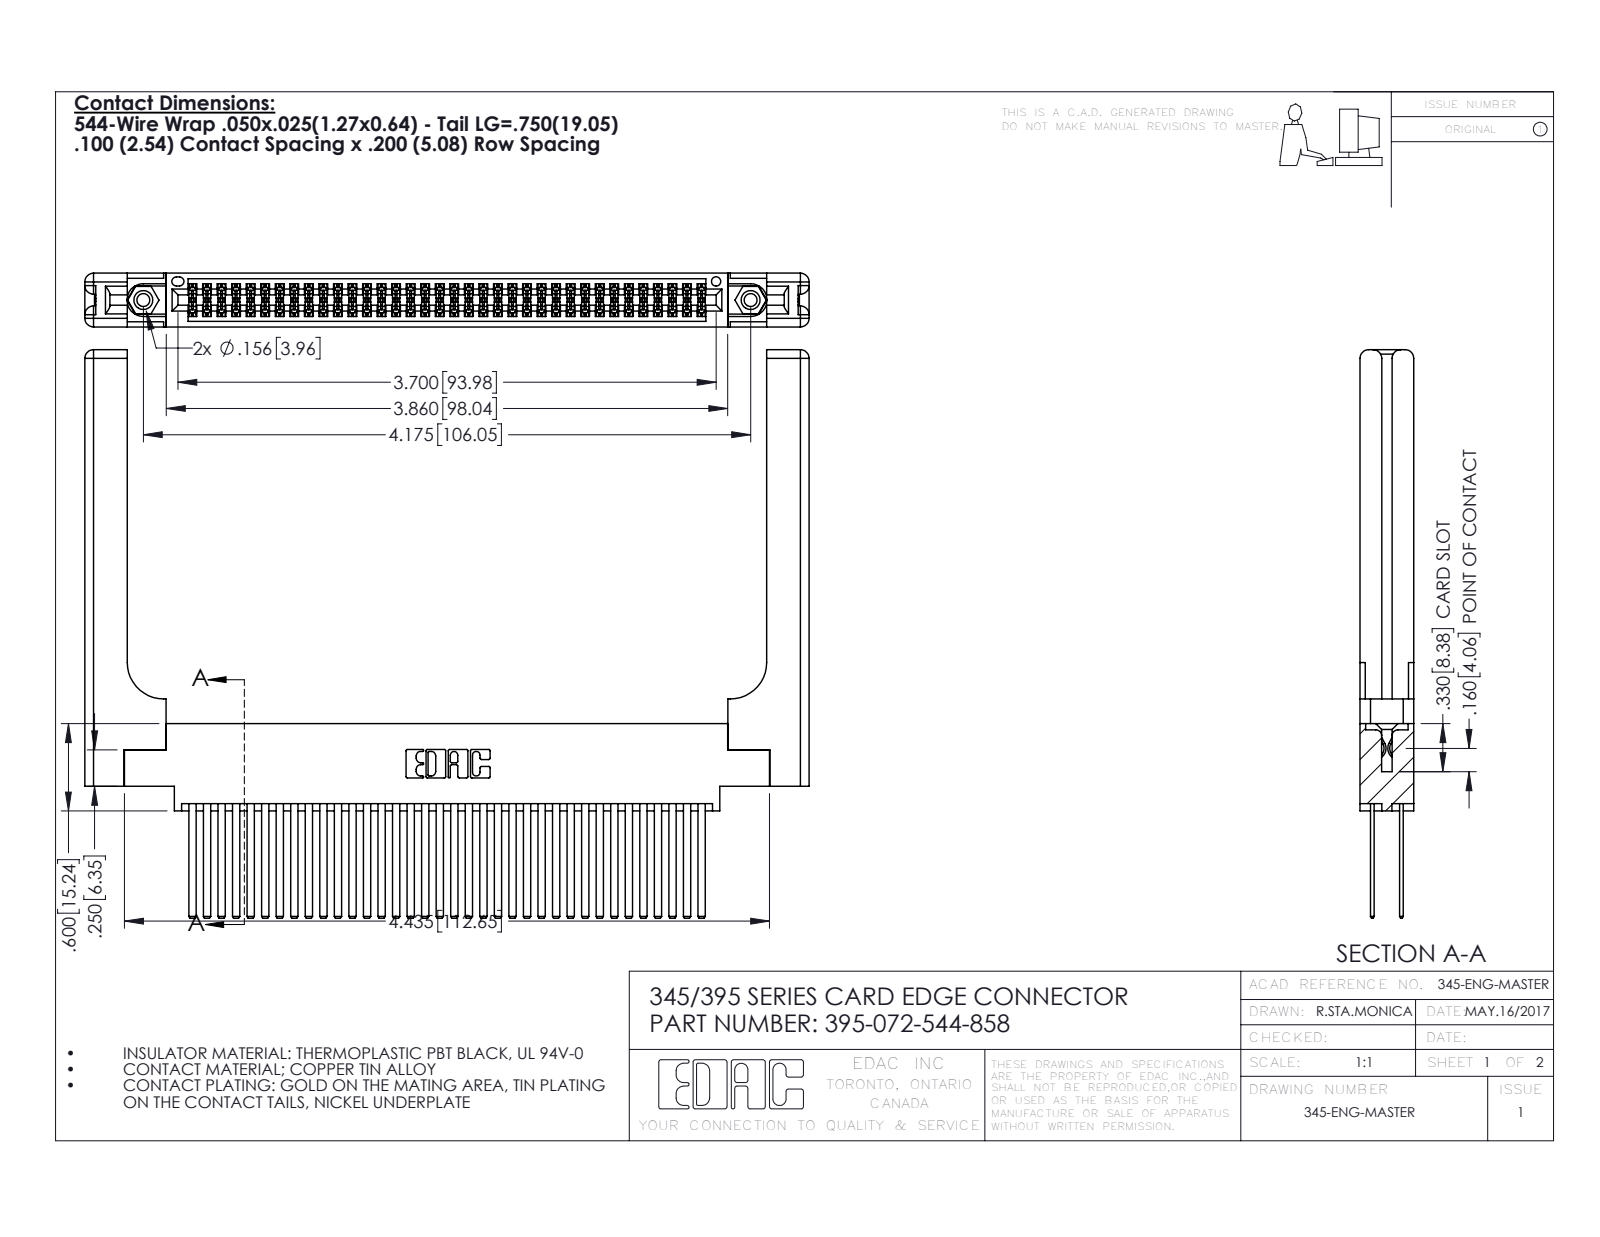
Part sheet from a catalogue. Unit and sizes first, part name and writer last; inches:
Units: inches
Overall size (bounding box): 4.979 × 3.907 × 0.37
Round holes (diameter × count): ⌀0.089 ×2, ⌀0.125 ×2, ⌀0.156 ×2, ⌀0.064 ×1
Round bosses / shafts (diameter × count): ⌀0.155 ×2
Partial cylindrical surfaces — rounded edges, fillets, slot ends (radius × count): R0.006 ×108, R0.01 ×22, R0.06 ×16, R0.007 ×6, R0.031 ×6, R0.026 ×3, R0.014 ×2, R0.019 ×2
Main face-to-face distances: 0.072, 0.298, 0.098, 0.272, 0.025, 0.2, 0.37, 0.225, 0.175, 0.148
Hole centre spacings: 0.27, 3.939, 4.175
Volume: 1.318 in³ · Surface area: 42.54 in²
Bodies: 77 solids, 3554 faces (2320 planar, 1174 cylindrical, 60 other)
Part name (STEP PRODUCT): 395-072-544-858; 345-292-001_345-293-144; 345-250-001_345-250-001-102; 345-220-058_345-220-058 (+1 more)
STEP written by: SolidWorks 2016 (CONFIG_CONTROL_DESIGN)
